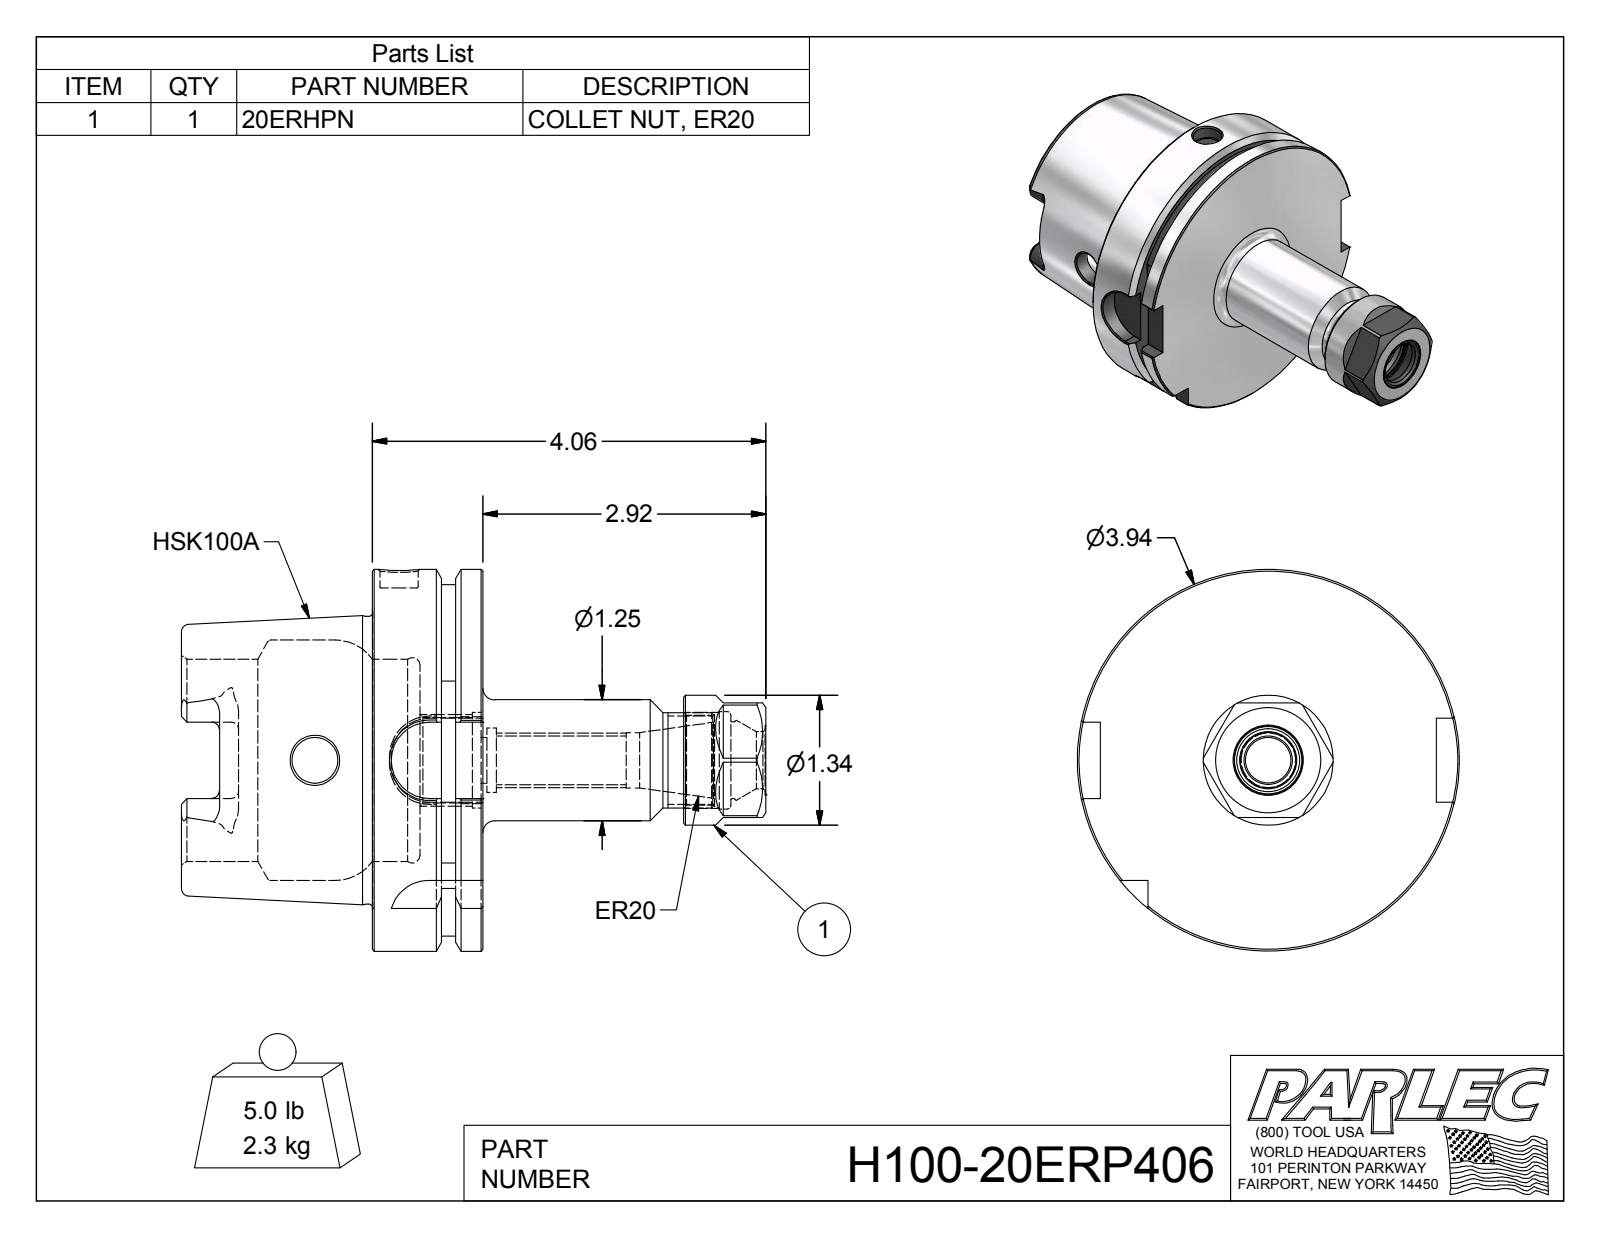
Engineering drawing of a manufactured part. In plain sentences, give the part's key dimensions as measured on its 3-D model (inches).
The part is named "H100-20ERP406; H100-20ER4-1; 20ERHPN". Its 3-D file was written by "Autodesk Inventor 2012 (AUTOMOTIVE_DESIGN)". It is 2 solids with 165 faces: 62 planar, 42 cylindrical and 61 other. Overall it measures 6.029 by 3.937 by 3.937 inches. Its volume is 18.13 cubic inches and its surface area 97.58 square inches. Round holes: 2 of diameter 0.472, 1 of diameter 0.394, 1 of diameter 0.472, 1 of diameter 0.502, 1 of diameter 0.57, 1 of diameter 0.587, 1 of diameter 0.663, 1 of diameter 0.79, 1 of diameter 0.881, 1 of diameter 0.926, 1 of diameter 0.985, 1 of diameter 1.005. Round bosses or shafts: 1 of diameter 3.937, 1 of diameter 2.967, 1 of diameter 1.34, 1 of diameter 1.25, 1 of diameter 0.984. Partial cylindrical surfaces (rounded edges, fillets, slot ends): 6 of radius 0.079, 4 of radius 0.192, 4 of radius 0.394, 1 of radius 1.811. The main face-to-face distances are 1.142, 0.492, 0.65, 1.969, 2.461, 3.11, 2.83, 0.861, 0.369, 0.28.
